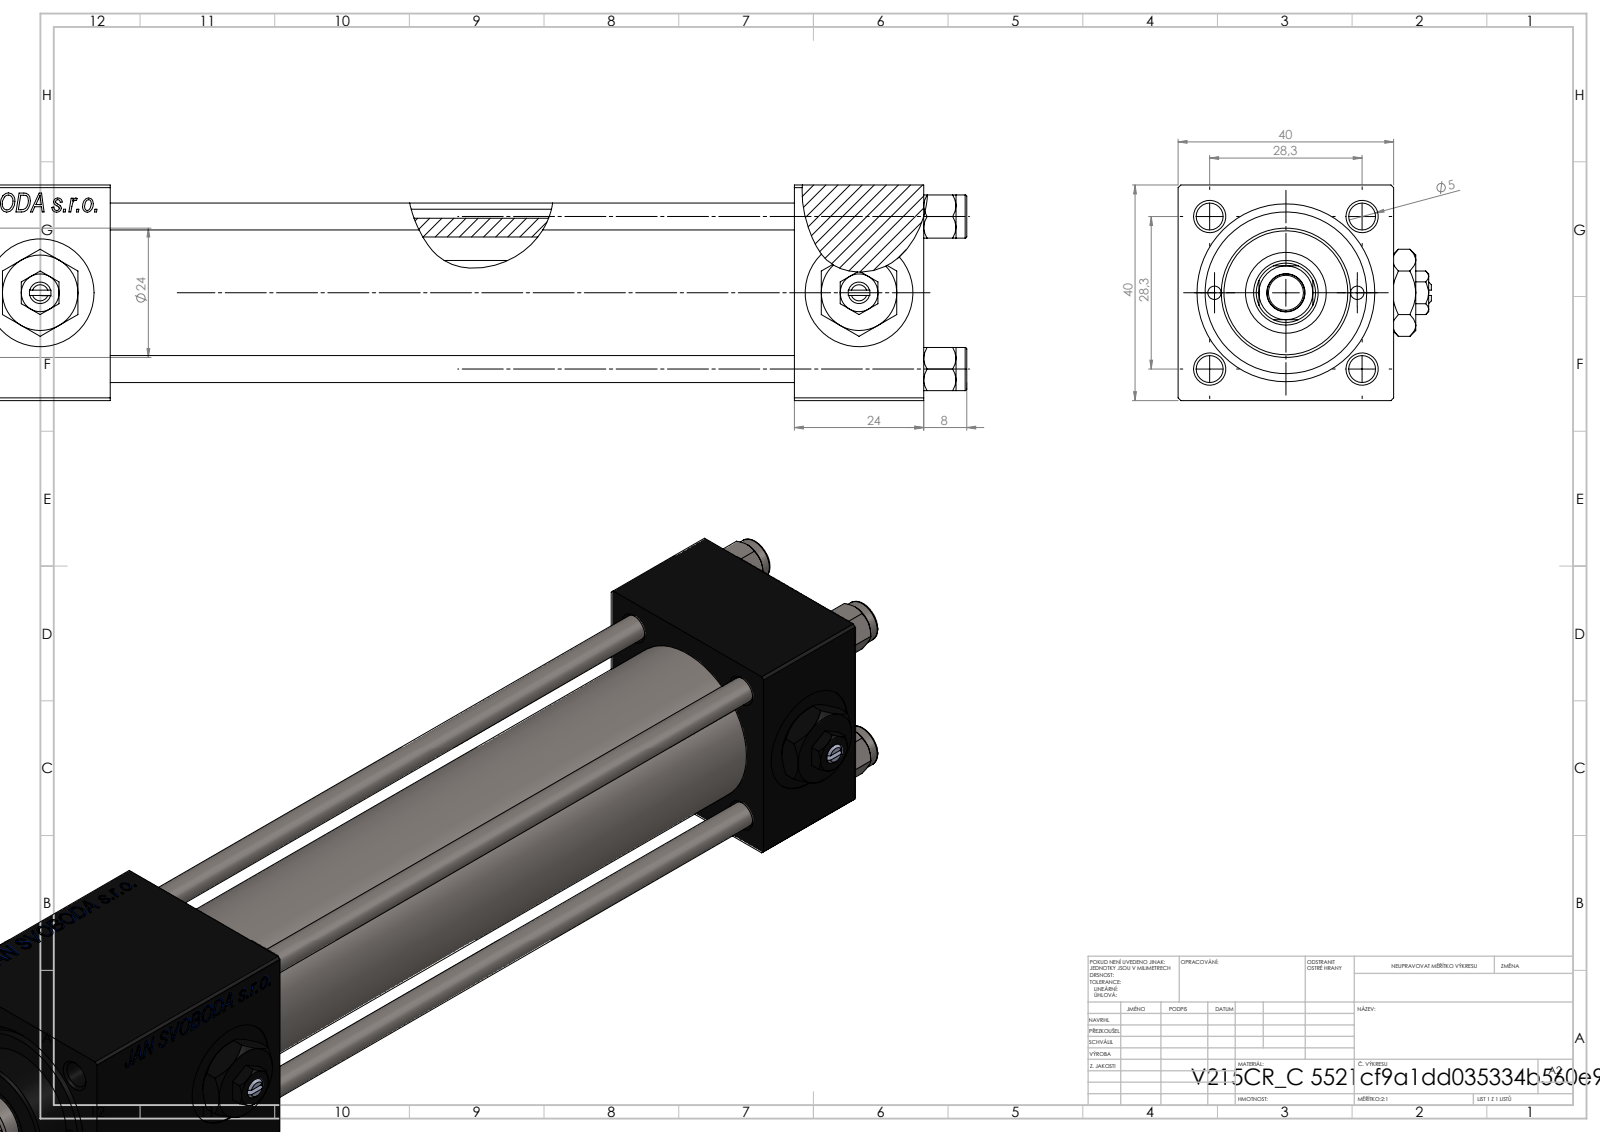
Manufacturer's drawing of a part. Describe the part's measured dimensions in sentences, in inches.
The part is named "V215_VC_A; V215CR_C_Body; V215CR_C_TYCINKA; NUT_M5_C (+2 more)". Its 3-D file was written by "SolidWorks 2019 (CONFIG_CONTROL_DESIGN)". It is 13 solids with 1254 faces: 574 planar, 102 cylindrical and 578 other. Overall it measures 8.74 by 1.85 by 1.575 inches. Its volume is 10.82 cubic inches and its surface area 121.5 square inches. Round holes: 4 of diameter 0.197, 3 of diameter 0.787, 2 of diameter 0.098, 2 of diameter 0.276, 2 of diameter 0.518, 1 of diameter 0.256, 1 of diameter 0.472, 1 of diameter 0.591, 1 of diameter 0.984, 1 of diameter 1.181. Round bosses or shafts: 4 of diameter 0.315, 1 of diameter 1.22, 1 of diameter 0.945. Partial cylindrical surfaces (rounded edges, fillets, slot ends): 1 of radius 0.217. The main face-to-face distances are 1.575, 0.945, 1.567, 6.705, 5.76, 1.89, 5.945, 5, 0.76, 6.89. The hole center spacings are 0.558, 0.788, 1.114, 1.214, 0.522, 1.576, 1.043, 5.984.
